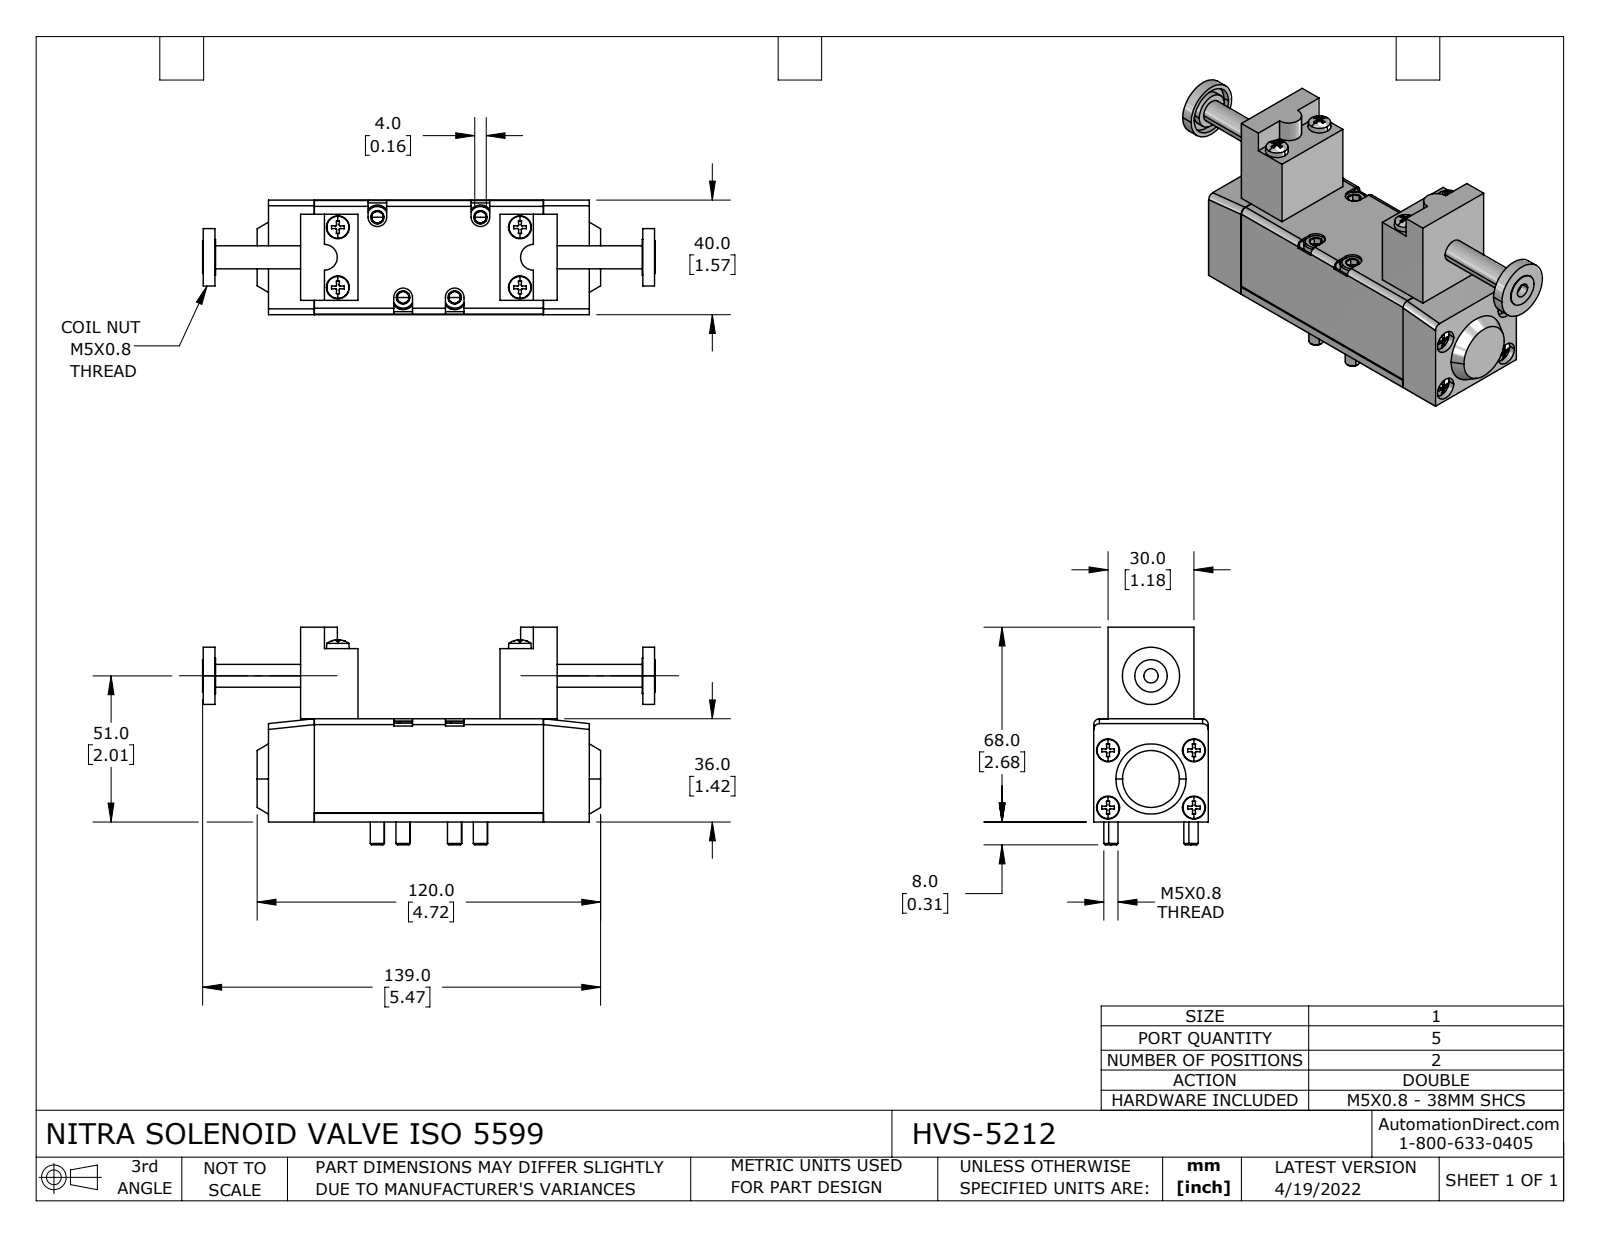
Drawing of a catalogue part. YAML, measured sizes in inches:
part_name: "HVS-5212"
step_written_by: "SolidWorks 2021 (CONFIG_CONTROL_DESIGN)"
units: inches
bodies: {solids: 21, faces: 850, planar: 434, cylindrical: 156, other: 260}
overall_size: [6.22, 2.992, 1.575]
volume: 12.18
surface_area: 84.18
round_holes:
  - {diameter: 0.128, count: 8}
  - {diameter: 0.161, count: 4}
  - {diameter: 0.217, count: 4}
  - {diameter: 0.315, count: 4}
  - {diameter: 0.197, count: 1}
  - {diameter: 0.665, count: 1}
round_bosses_or_shafts:
  - {diameter: 0.157, count: 8}
  - {diameter: 0.335, count: 4}
  - {diameter: 0.197, count: 4}
  - {diameter: 0.787, count: 1}
  - {diameter: 0.488, count: 1}
  - {diameter: 0.445, count: 1}
  - {diameter: 0.315, count: 1}
partial_cylinders:
  - {radius: 0.079, count: 6}
  - {radius: 0.128, count: 4}
  - {radius: 0.197, count: 4}
  - {radius: 0.177, count: 2}
face_to_face_distances: [0.189, 1.417, 3.15, 1.567, 1.559, 3.339, 0.197, 1.378, 1.37, 0.787]
hole_center_spacings: [0.561, 0.787, 0.827, 0.908, 1.107, 1.158, 1.181, 1.182]
